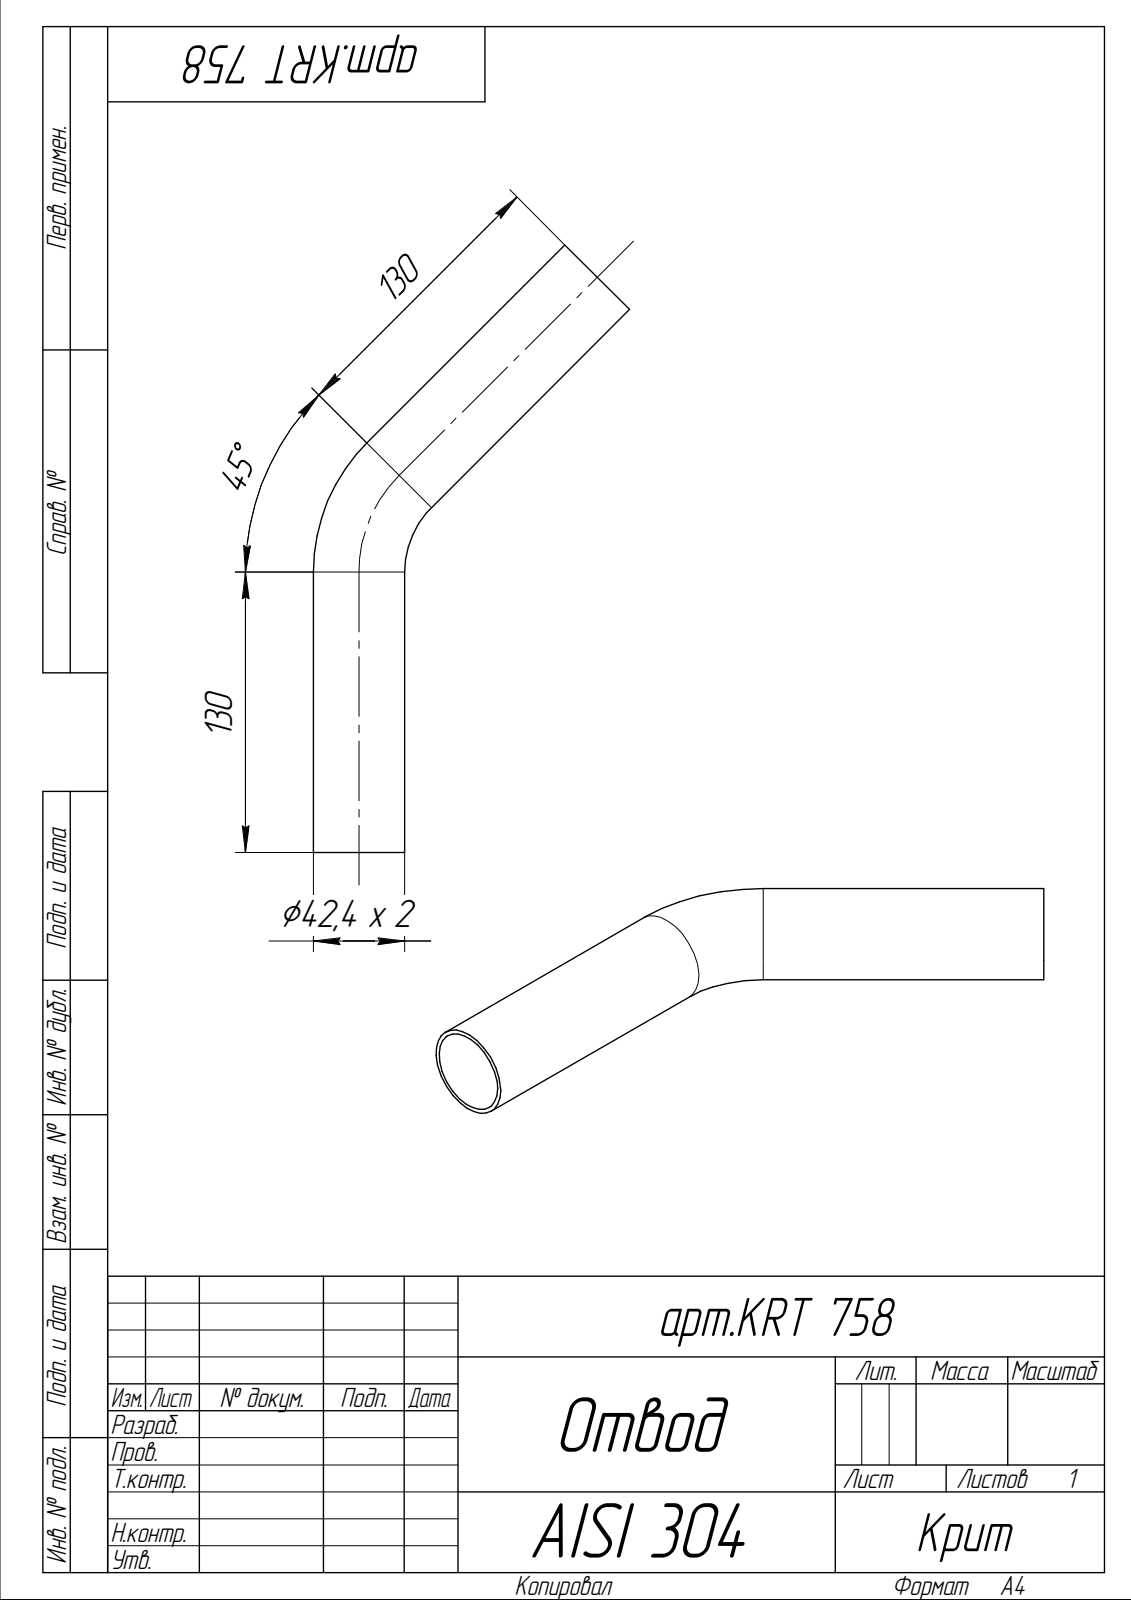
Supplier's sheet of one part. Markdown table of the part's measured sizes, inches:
| quantity | value |
| --- | --- |
| part name | Деталь |
| STEP written by | ASCON Math Kernel (AUTOMOTIVE_DESIGN) |
| units | inches |
| bodies | 1 solid, 8 faces (2 planar, 4 cylindrical, 2 other) |
| overall size | 11.098 × 5.777 × 1.669 |
| volume | 4.801 in³ |
| surface area | 122.7 in² |
| round holes (diameter × count) | 1.512 × 2 |
| round bosses / shafts (diameter × count) | 1.669 × 2 |
